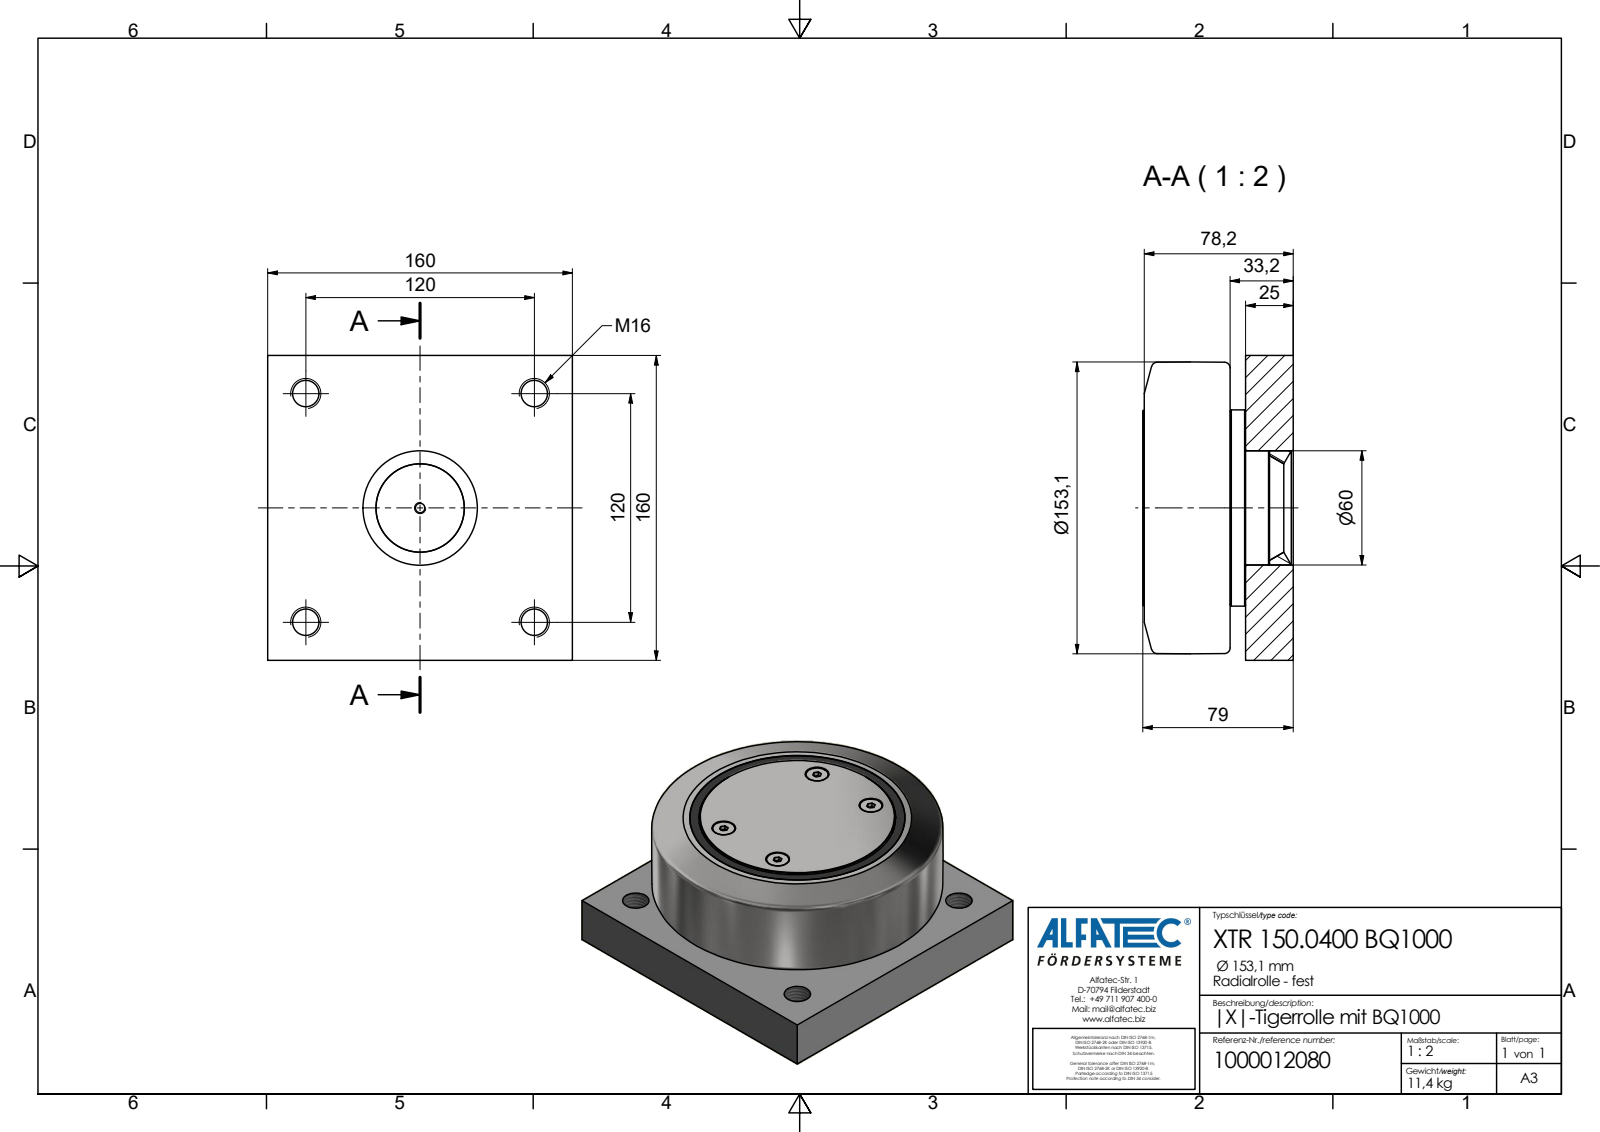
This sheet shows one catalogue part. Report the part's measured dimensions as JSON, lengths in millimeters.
{"part_name": "XTR 150.0400 BQ1000_Kontur", "step_written_by": "Autodesk Inventor 2020 (AP242_MANAGED_MODEL_BASED_3D_ENGINEERING_MIM_LF)", "units": "millimeters", "bodies": {"solids": 1, "faces": 72, "planar": 46, "cylindrical": 15, "other": 11}, "overall_size": [160, 160, 79], "volume_mm3": 1509000, "surface_area_mm2": 112942, "round_holes": [[12.4, 4], [13.84, 4]], "round_bosses_or_shafts": [[11.7, 4], [103, 1], [102.5, 1], [101.4, 1]], "face_to_face_distances": [25, 33.2, 8.2, 160, 79, 54, 45.8, 78.2, 53.2, 45], "hole_center_spacings": [47.36, 83.92, 102.75, 120, 123.92, 40, 69.28, 80]}
